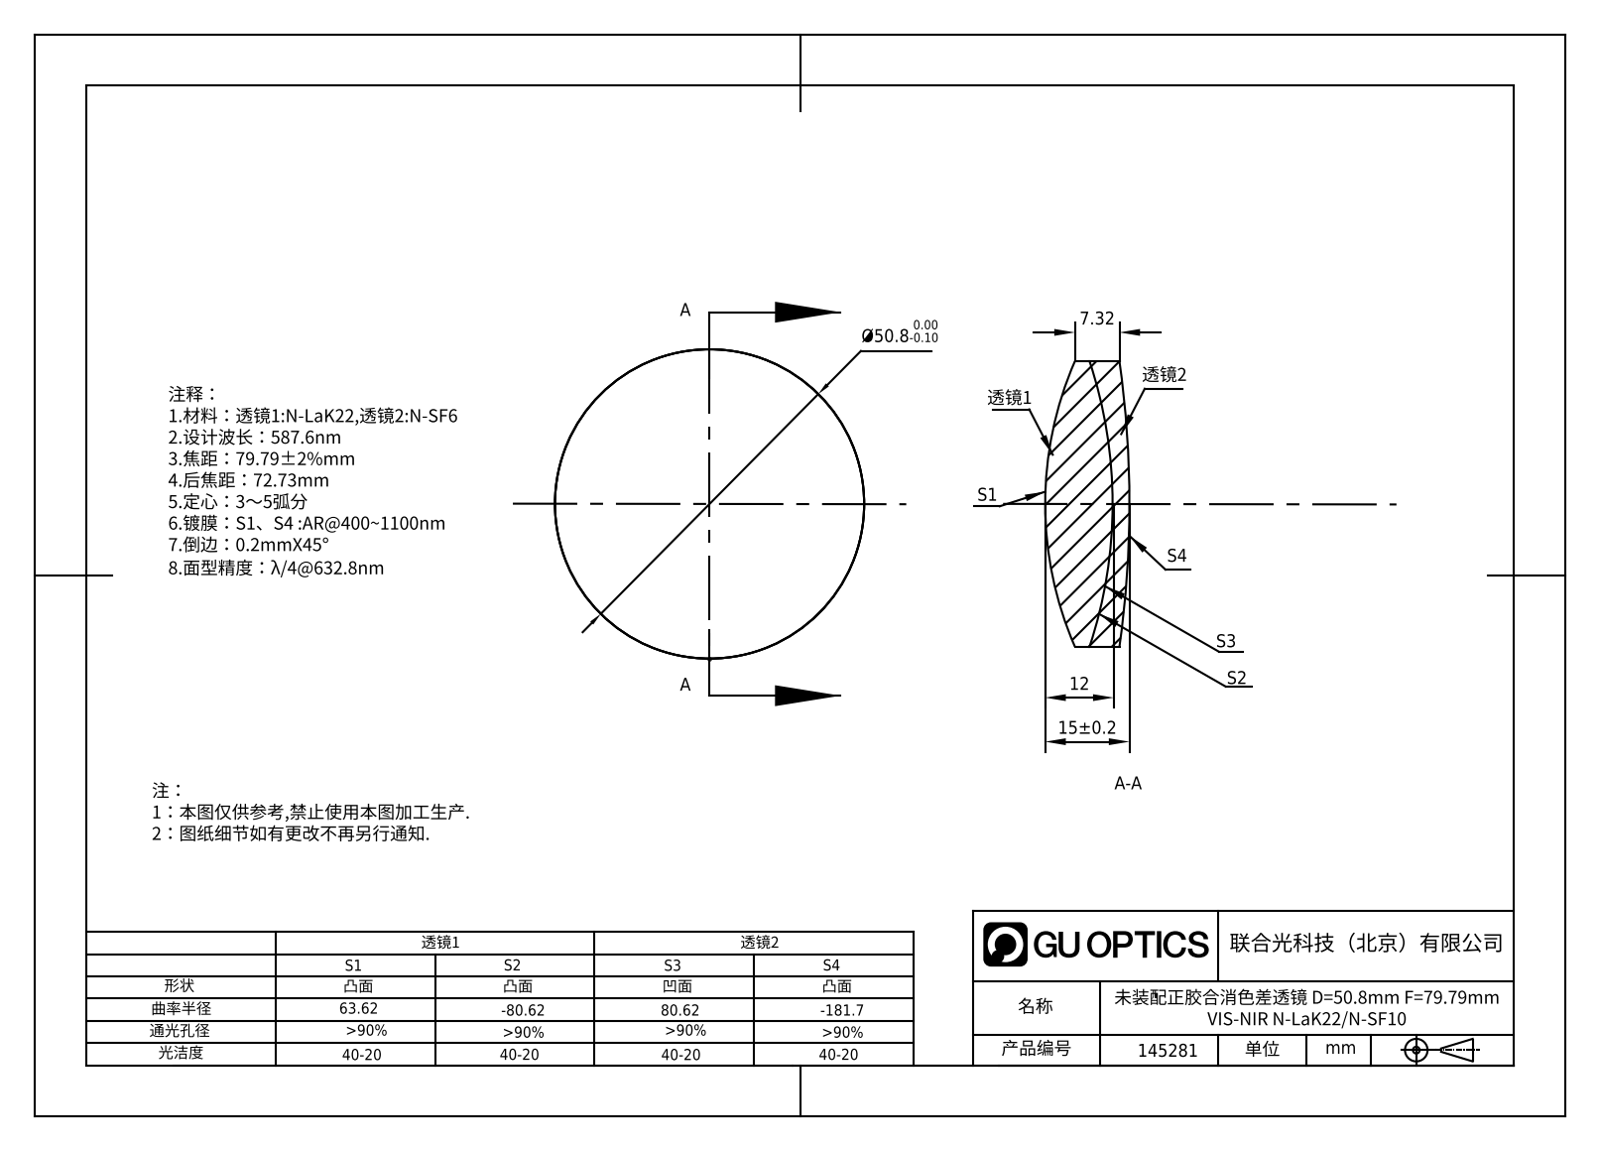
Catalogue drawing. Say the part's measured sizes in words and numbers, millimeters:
The part is named "145281". Its 3-D file was written by "SolidWorks 2020 (CONFIG_CONTROL_DESIGN)". It is 2 solids with 12 faces: 0 planar, 4 cylindrical and 8 other. Overall it measures 50.8 by 50.8 by 15 millimeters. Its volume is 23 314 cubic millimeters and its surface area 9 576 square millimeters. Round bosses or shafts: 1 of diameter 50.8.
